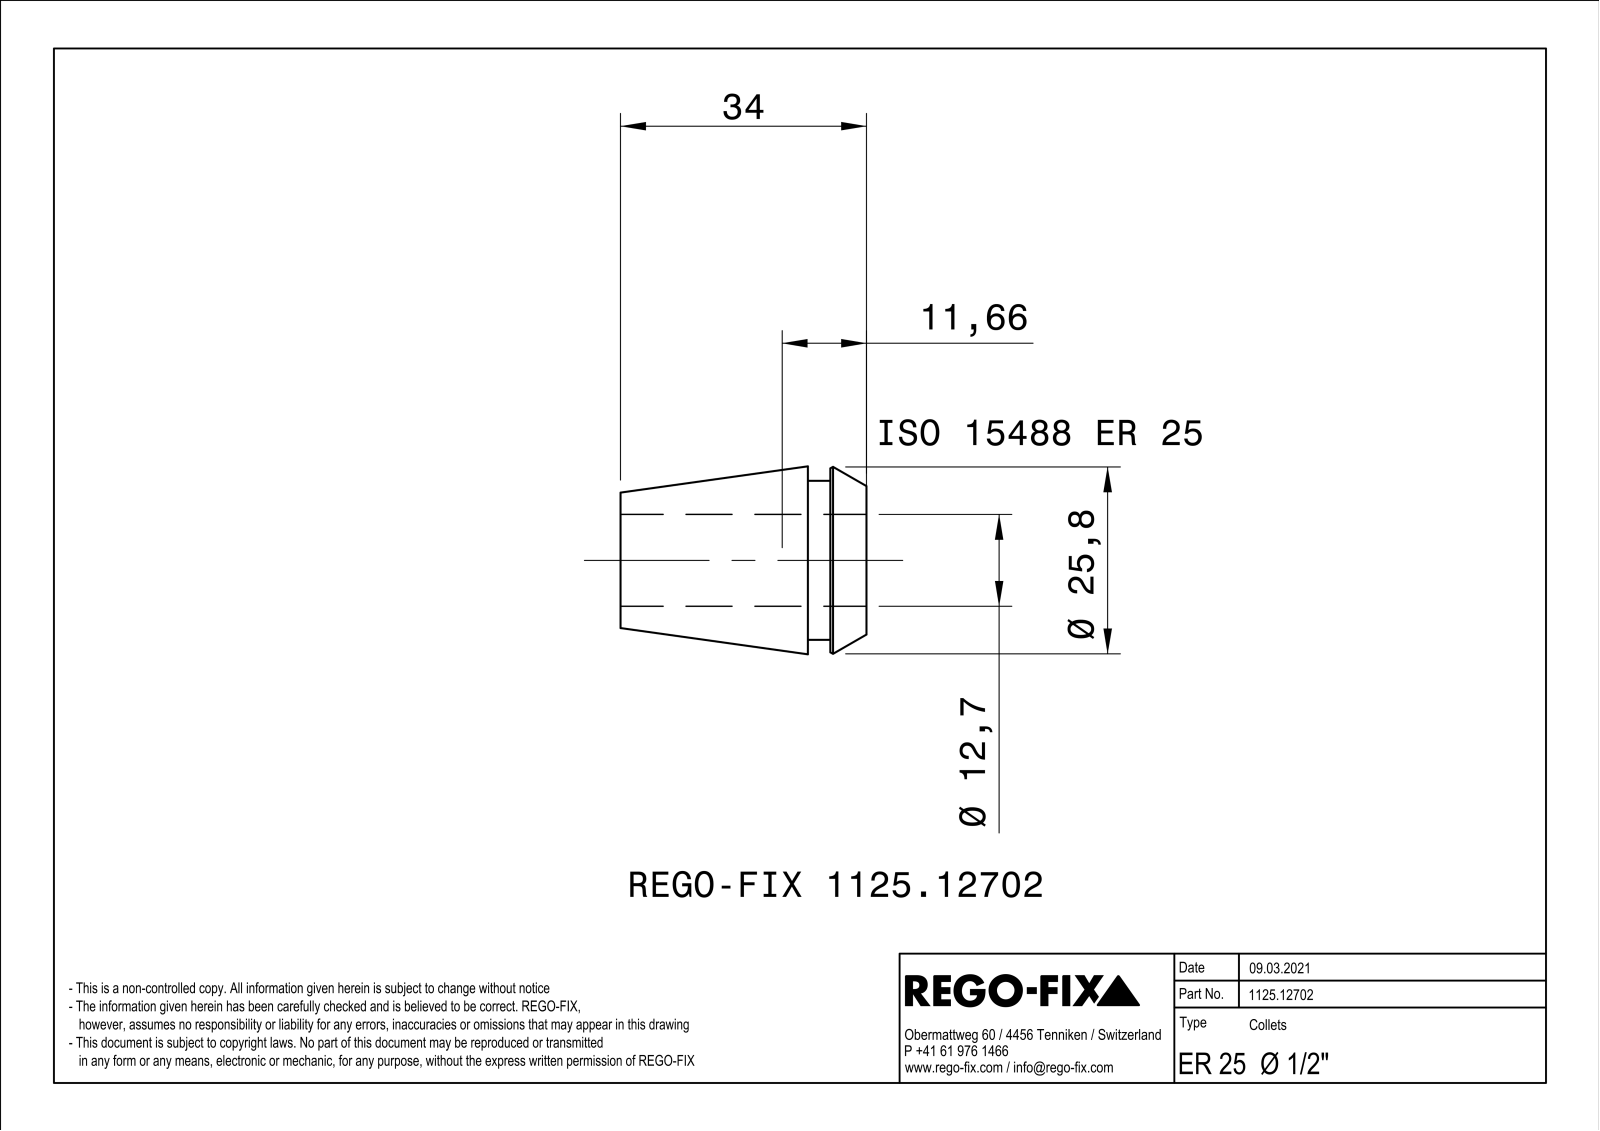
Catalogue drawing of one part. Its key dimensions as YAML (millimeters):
part_name: "NOCUT"
step_written_by: "SIEMENS PLM Software Solid Edge ST10 (AUTOMOTIVE_DESIGN)"
units: millimeters
bodies: {solids: 1, faces: 177, planar: 72, cylindrical: 25, other: 80}
overall_size: [34, 25.99, 25.99]
volume: 7412
surface_area: 8327
round_holes:
  - {diameter: 12.7, count: 1}
round_bosses_or_shafts:
  - {diameter: 22, count: 1}
partial_cylinders:
  - {radius: 0.4, count: 8}
face_to_face_distances: [0.8, 8.1, 34, 25.9, 5, 3.1, 29]
